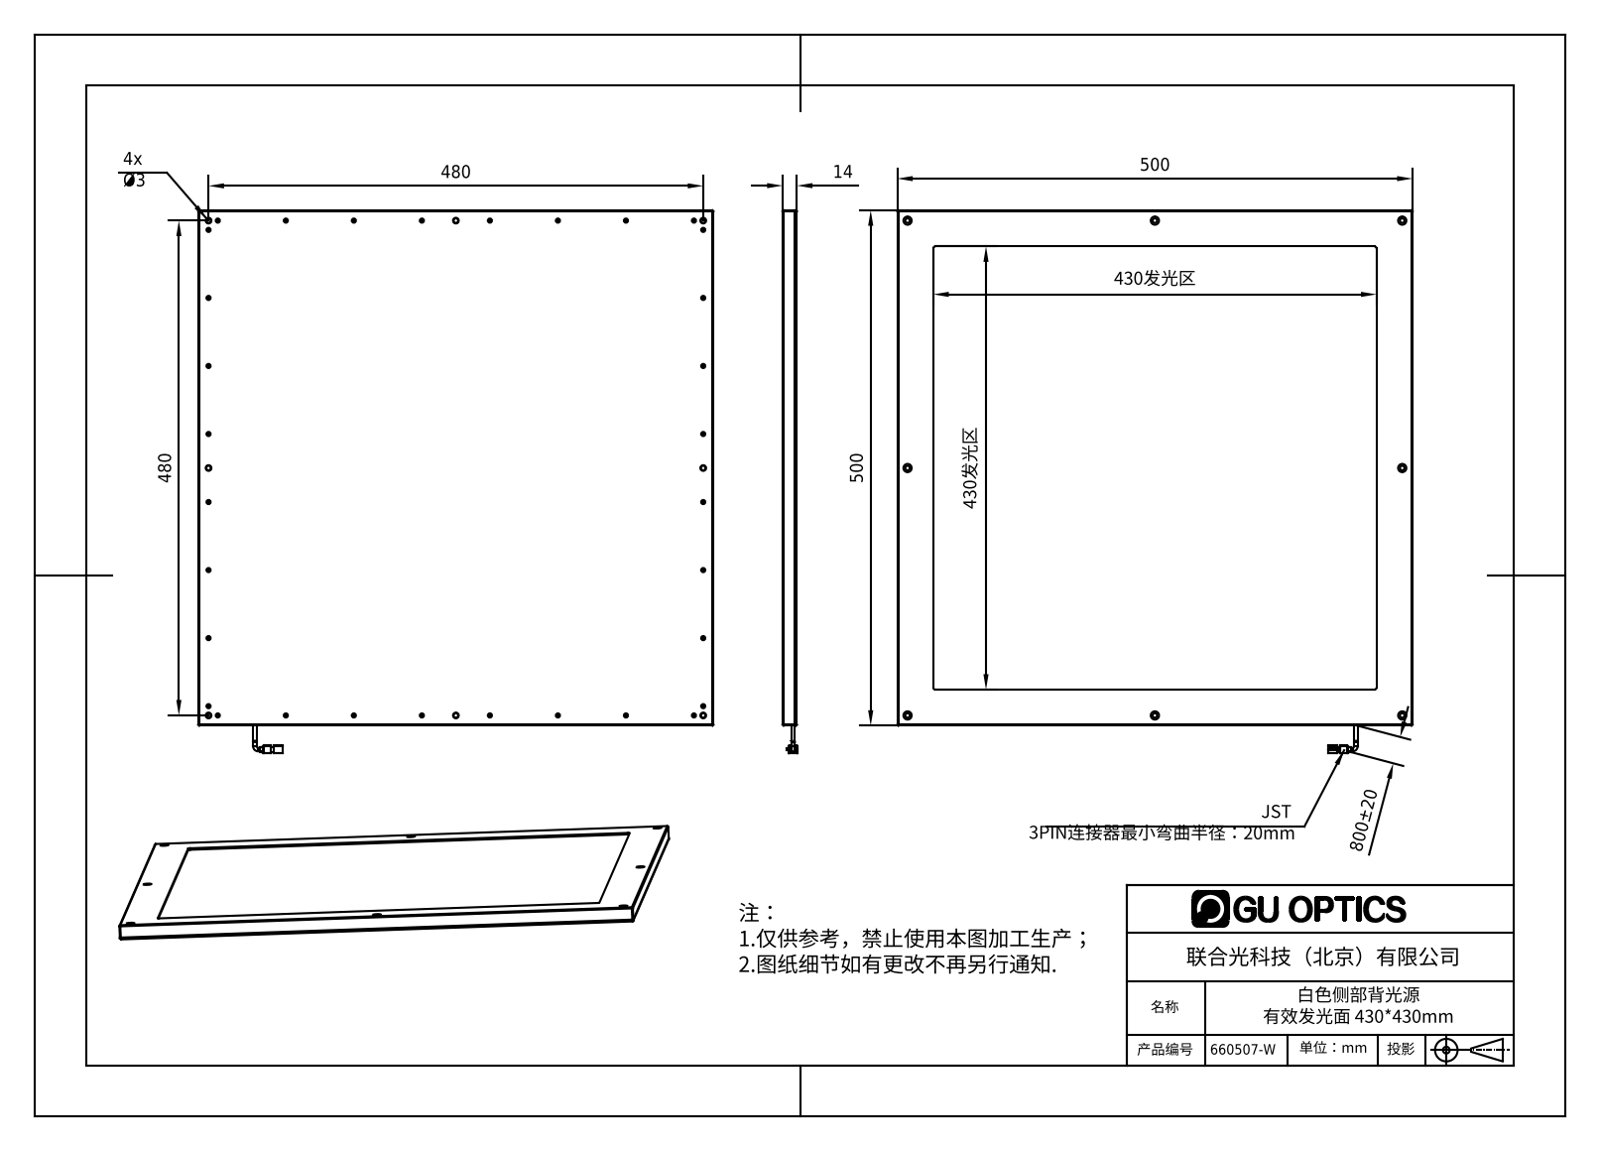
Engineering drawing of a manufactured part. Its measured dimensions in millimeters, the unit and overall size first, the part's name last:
Units: millimetres
Overall size (bounding box): 527 × 500 × 14.15
Round holes (diameter × count): ⌀1.6 ×32, ⌀2.4 ×32, ⌀4.5 ×8, ⌀8 ×8
Round bosses / shafts (diameter × count): ⌀3.5 ×2
Partial cylindrical surfaces — rounded edges, fillets, slot ends (radius × count): R2 ×9, R0.5 ×8, R1 ×4, R1.8 ×1
Main face-to-face distances: 2, 12, 10, 14, 0.5, 1.5, 10.5, 12.5, 20, 480
Hole centre spacings: 66, 484.52, 132, 497.82, 198, 519.23, 264, 480
Volume: 3 088 000 mm³ · Surface area: 1 120 000 mm²
Bodies: 5 solids, 592 faces (176 planar, 211 cylindrical, 205 other)
Part name (STEP PRODUCT): 660507-W
STEP written by: SolidWorks 2016 (AUTOMOTIVE_DESIGN)
